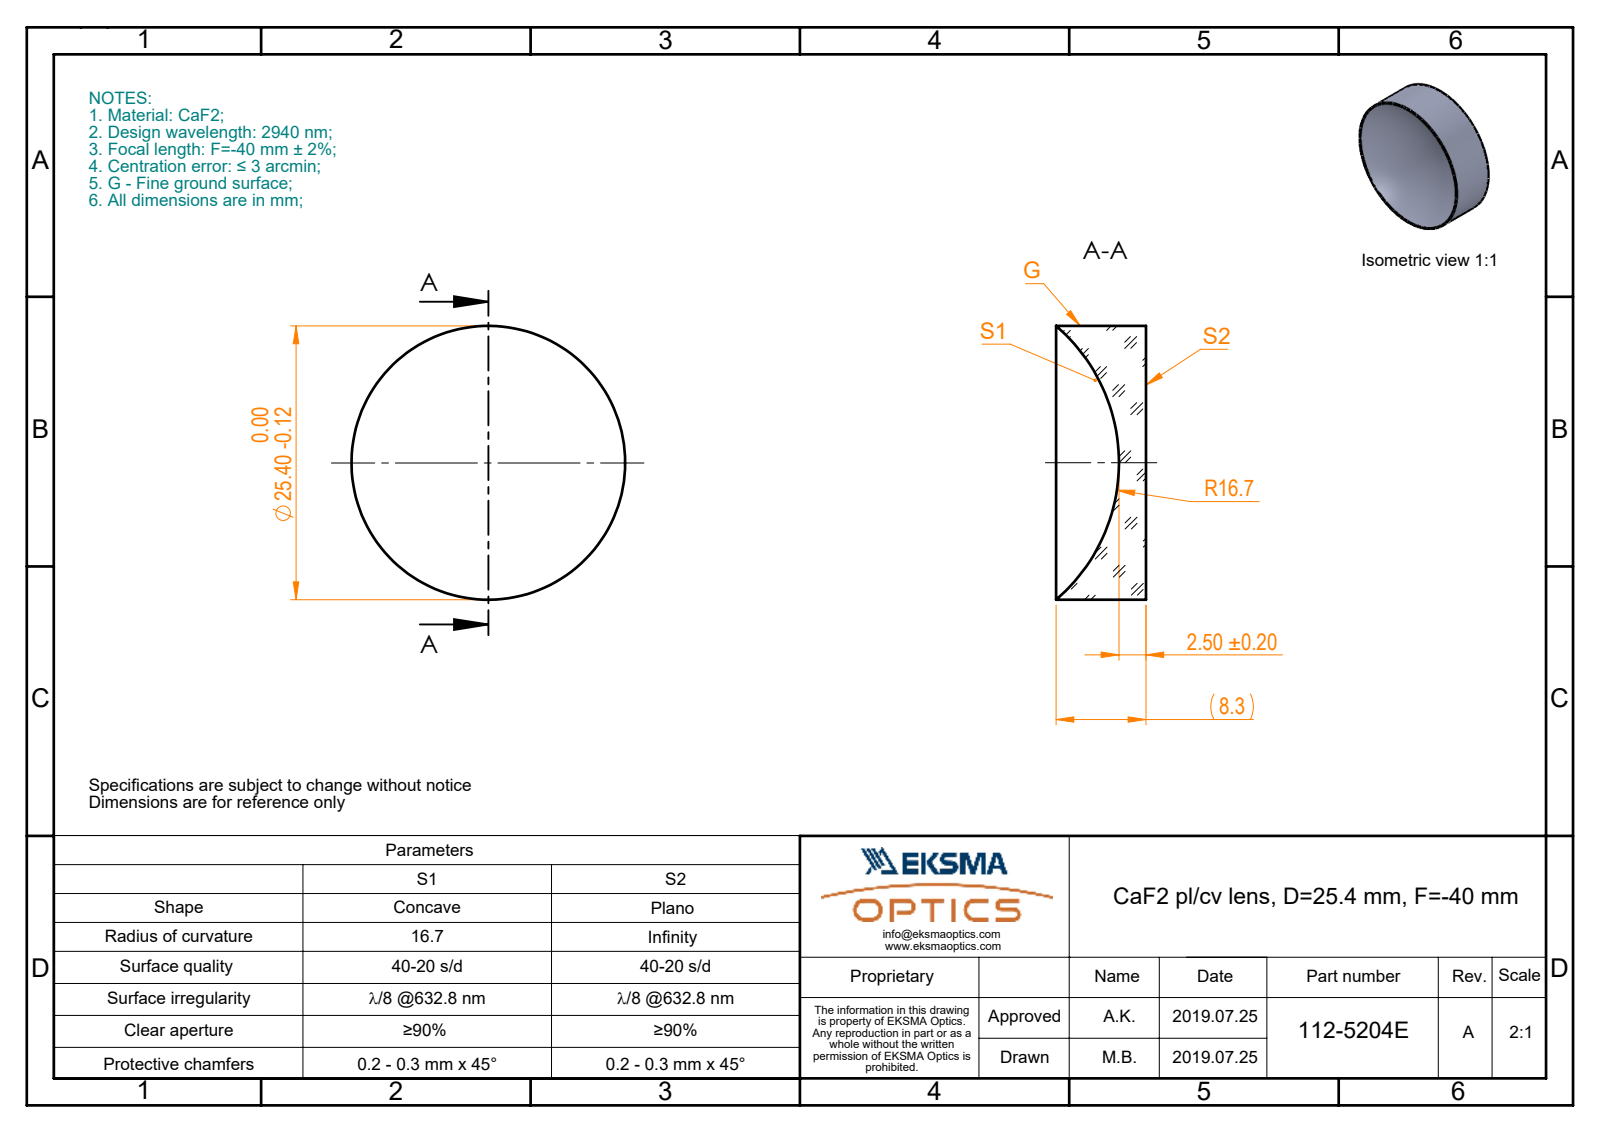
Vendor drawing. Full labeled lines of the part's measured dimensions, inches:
Part name (STEP PRODUCT): 112-5204E CaF2 pl-cv 12.7 F-40
STEP written by: SolidWorks 2017 (CONFIG_CONTROL_DESIGN)
Units: inches
Bodies: 1 solid, 5 faces (1 planar, 2 cylindrical, 2 other)
Overall size (bounding box): 1 × 1 × 0.328
Volume: 0.161 in³ · Surface area: 2.768 in²
Round bosses / shafts (diameter × count): ⌀1 ×1
